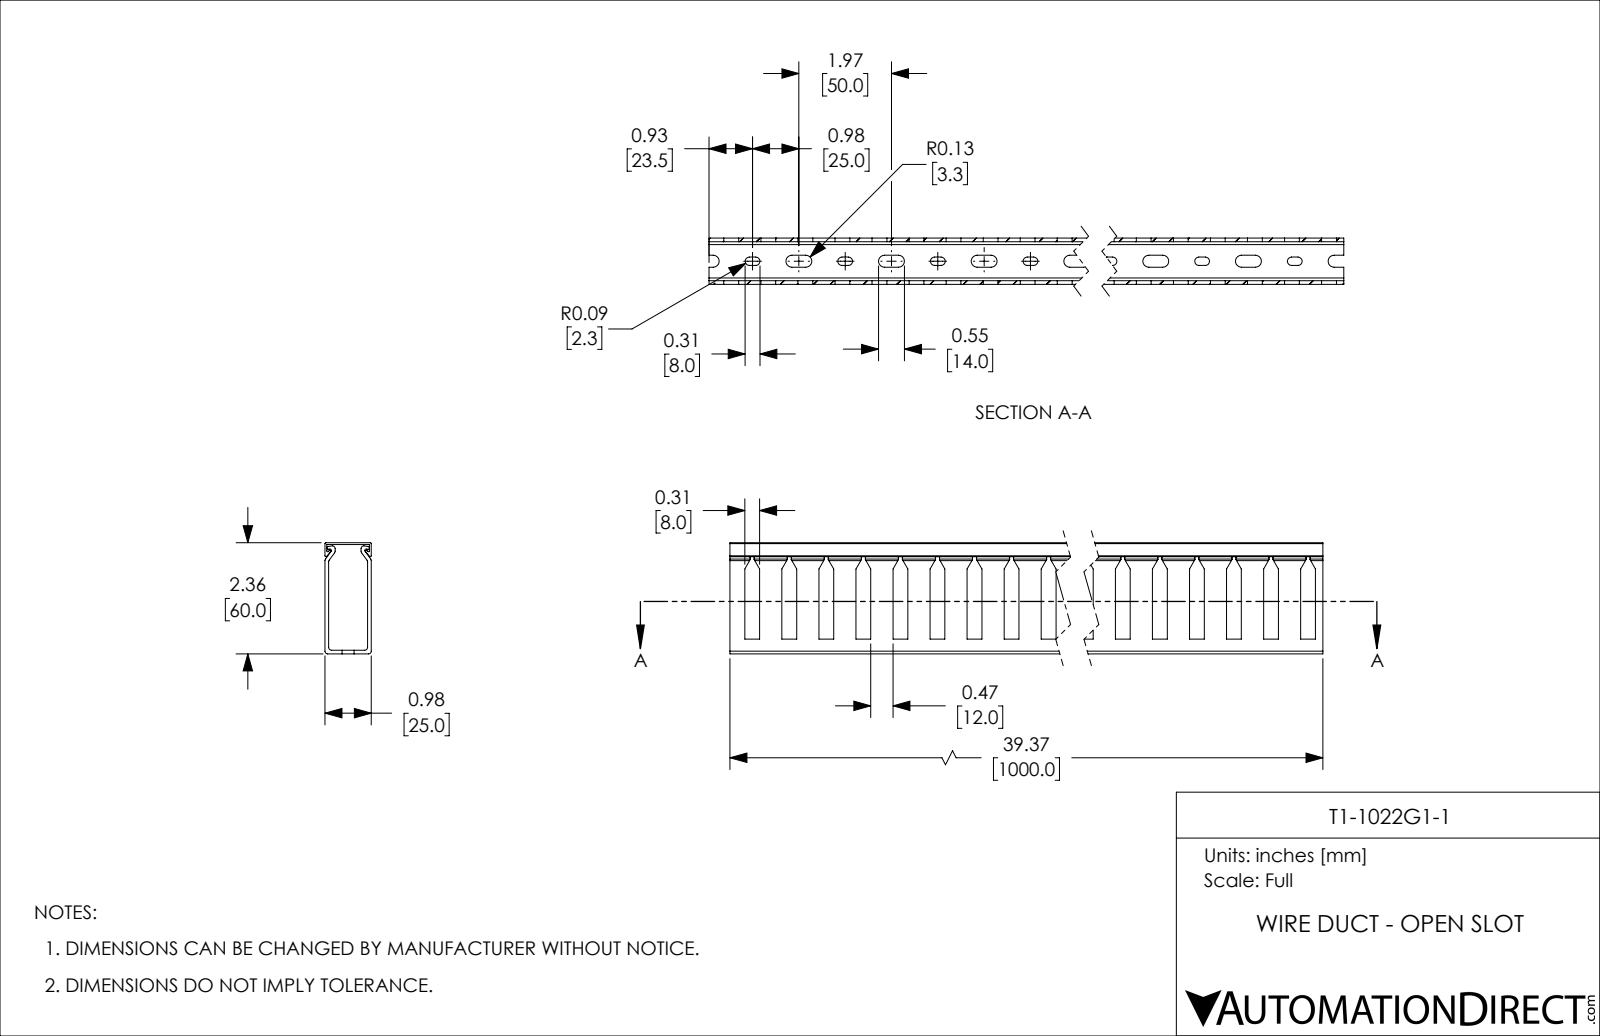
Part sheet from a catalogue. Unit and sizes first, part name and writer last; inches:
Units: inches
Overall size (bounding box): 39.37 × 2.362 × 0.984
Partial cylindrical surfaces — rounded edges, fillets, slot ends (radius × count): R0.089 ×40, R0.128 ×40, R0.059 ×12, R0.02 ×8, R0.03 ×6
Main face-to-face distances: 0.079, 0.906, 0.984, 0.827, 0.039, 2.362, 2.323, 2.244, 2.283, 0.945
Volume: 18.95 in³ · Surface area: 556.5 in²
Bodies: 2 solids, 745 faces (434 planar, 311 cylindrical, 0 other)
Part name (STEP PRODUCT): T1-1022G1-1
STEP written by: SolidWorks 2021 (CONFIG_CONTROL_DESIGN)
